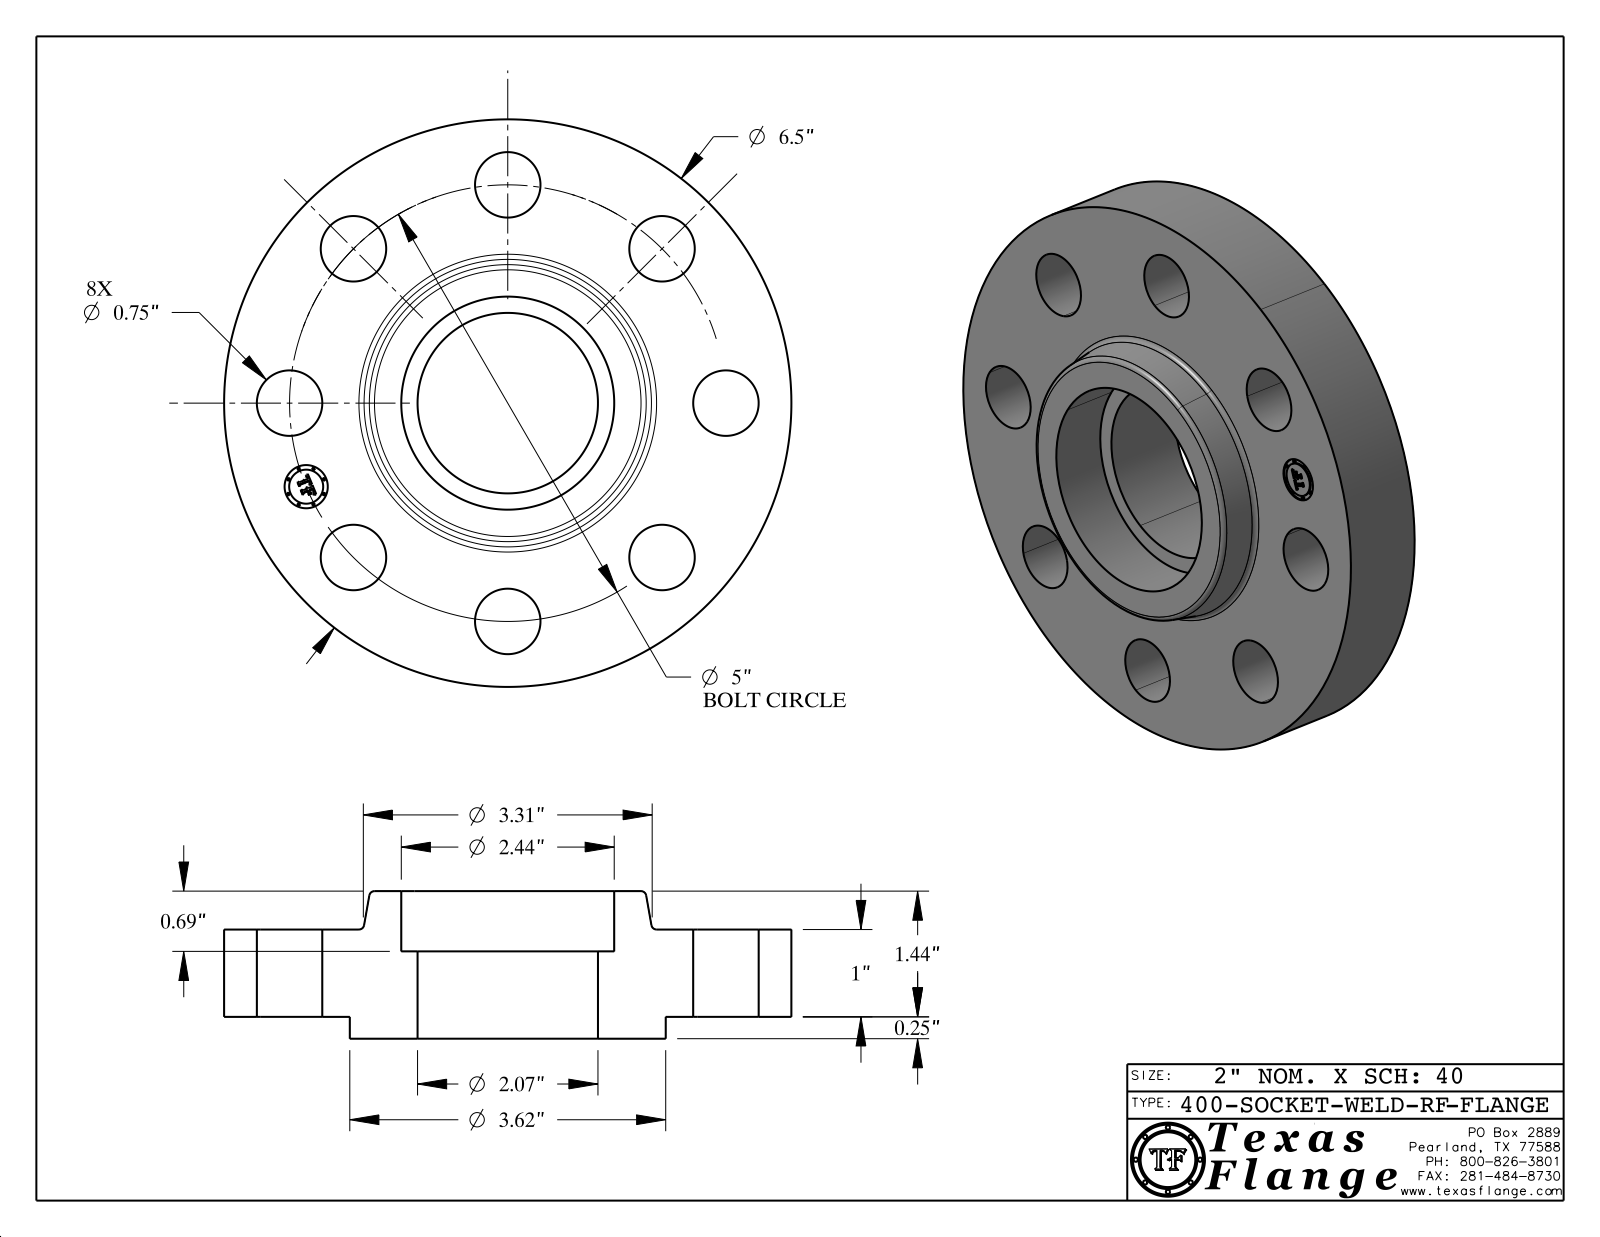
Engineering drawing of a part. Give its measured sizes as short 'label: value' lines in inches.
name: 400-SOCKET-WELD-RF
written by: CATIA V5 STEP AP214 (AUTOMOTIVE_DESIGN)
unit: in
bodies: 1 solid, 420 faces (370 planar, 44 cylindrical, 6 other)
size: 6.5 × 6.5 × 1.69
volume: 29.25 in³; area: 110 in²
holes: 8× ⌀0.75, 1× ⌀0.495, 1× ⌀2.067, 1× ⌀2.44
bosses: 8× ⌀0.03, 1× ⌀6.5, 1× ⌀3.62, 1× ⌀0.39
face distances: 1, 0.25, 1.25, 1.69, 1.44, 0.44, 0.75, 0.69, 1.235, 0.985
hole spacings: 2.5, 1.913, 3.535, 4.619, 5, 0.976, 2.778, 4.157
